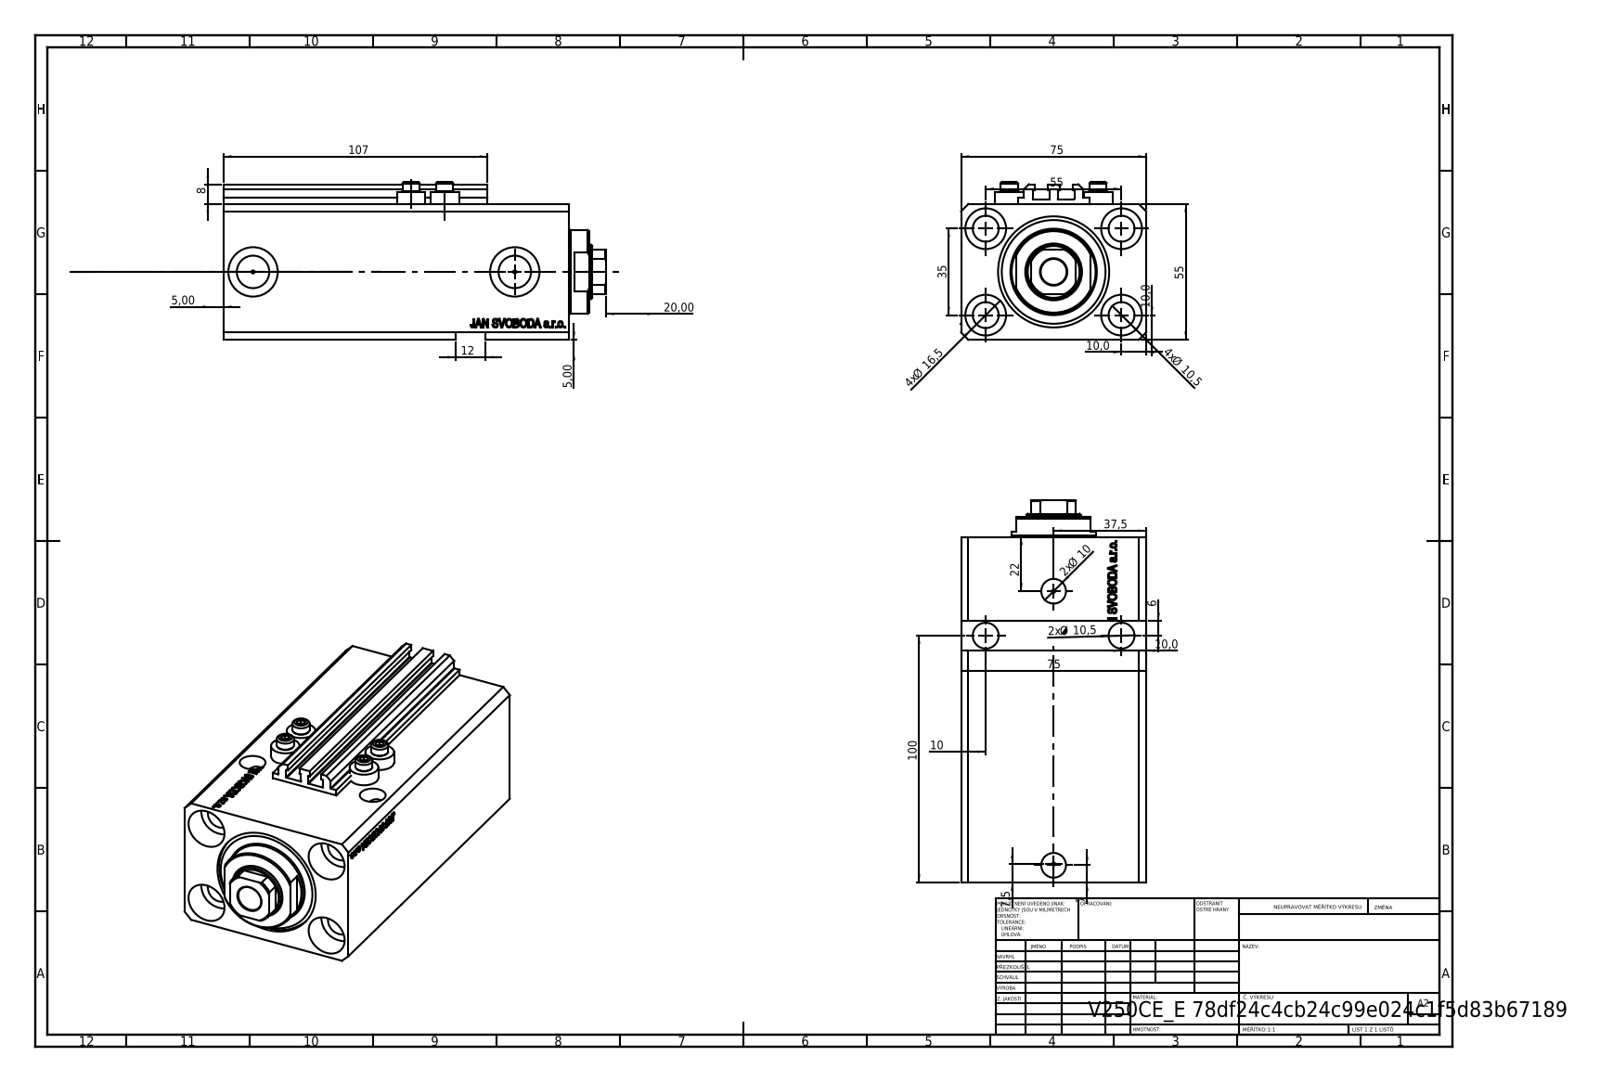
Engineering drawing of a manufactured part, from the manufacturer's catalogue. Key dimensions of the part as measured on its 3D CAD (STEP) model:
Part name (STEP PRODUCT): ALLEN BOLT V250CE; V250CE_E_Body; V250CE_VC_E; V250CE_C_VCP
STEP written by: SolidWorks 2019 (CONFIG_CONTROL_DESIGN)
Units: millimetres
Bodies: 8 solids, 1064 faces (514 planar, 126 cylindrical, 424 other)
Overall size (bounding box): 154.9 × 75 × 64
Volume: 491 635 mm³ · Surface area: 116 388 mm²
Round holes (diameter × count): ⌀10.5 ×7, ⌀1.25 ×4, ⌀4 ×4, ⌀16.5 ×4, ⌀10 ×2, ⌀13.16 ×2, ⌀20 ×2, ⌀22 ×1, ⌀32 ×1, ⌀45 ×1
Round bosses / shafts (diameter × count): ⌀11.6 ×4, ⌀7 ×4, ⌀34 ×1
Partial cylindrical surfaces — rounded edges, fillets, slot ends (radius × count): R0.2 ×10, R10.5 ×1
Main face-to-face distances: 55, 75, 140, 112.9, 27.1, 3, 9.9, 57, 103, 130.1
Hole centre spacings: 32.6, 55, 13.6, 14.09, 25.81, 32.87, 33.62, 35
